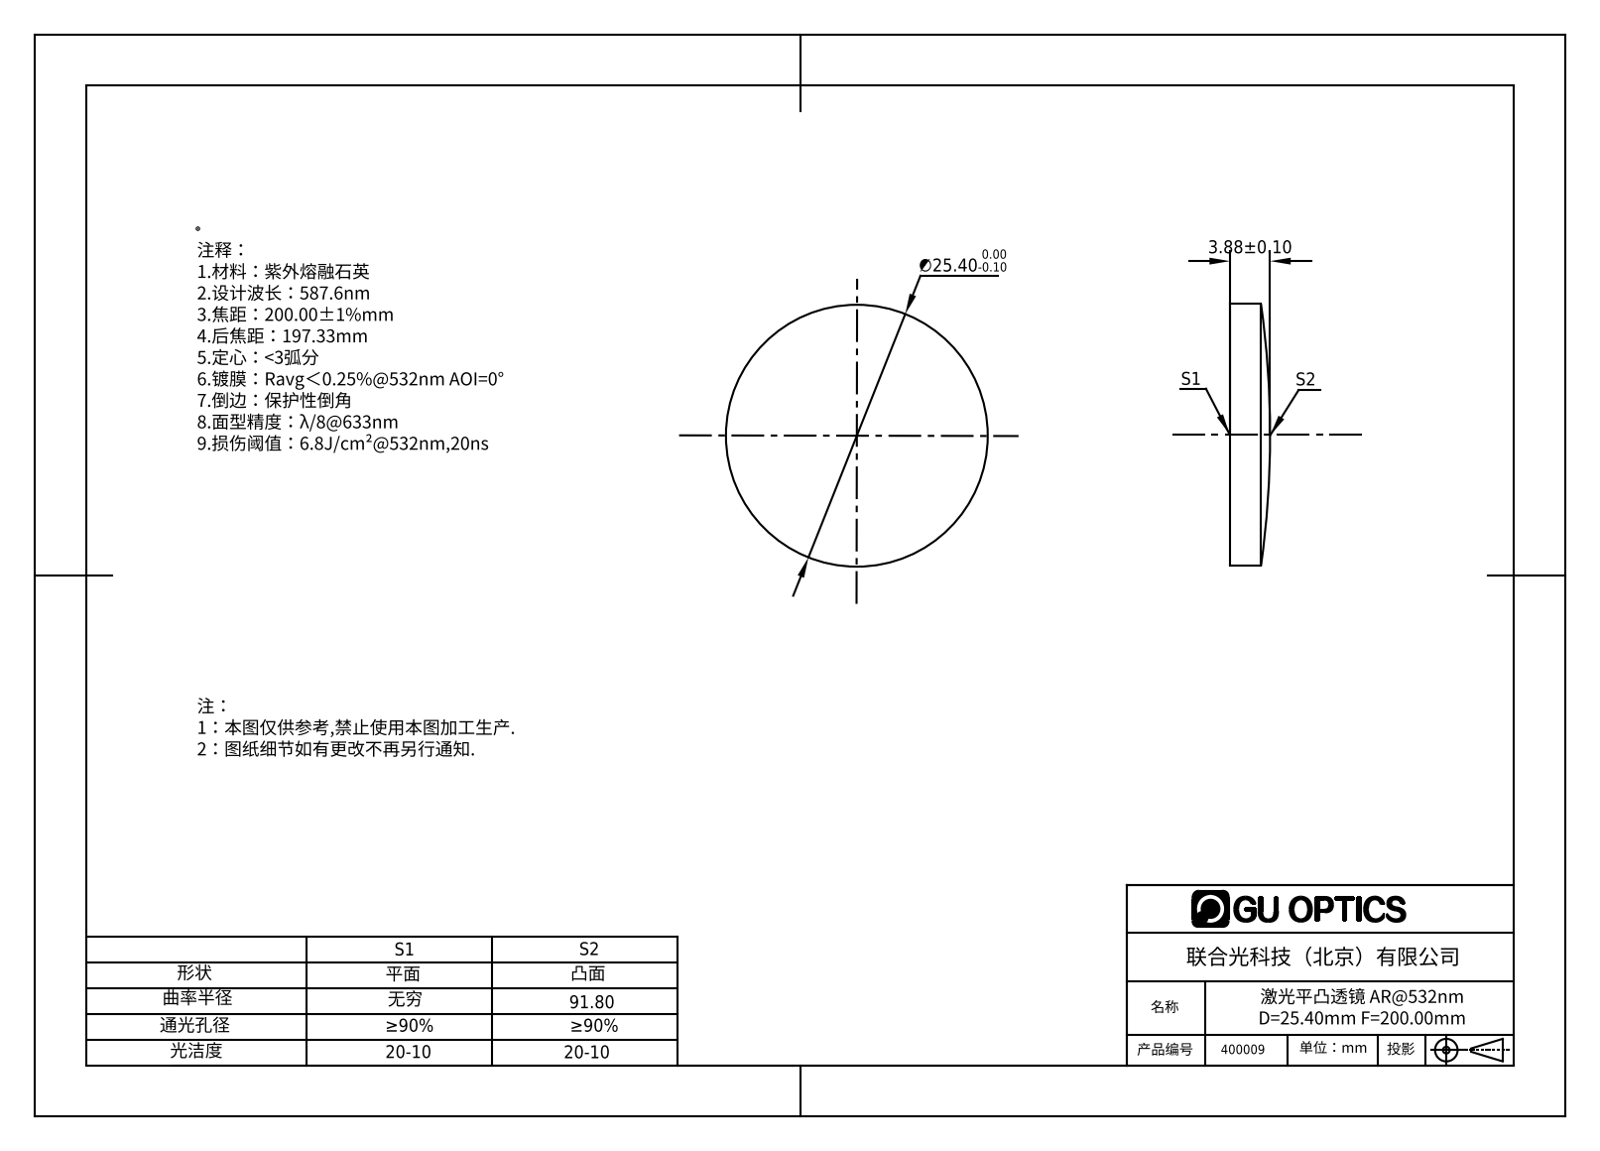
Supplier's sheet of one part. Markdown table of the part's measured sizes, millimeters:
| quantity | value |
| --- | --- |
| part name | 400003 |
| STEP written by | SolidWorks 2016 (AUTOMOTIVE_DESIGN) |
| units | millimeters |
| bodies | 1 solid, 5 faces (1 planar, 2 cylindrical, 2 other) |
| overall size | 25.4 × 25.4 × 3.88 |
| volume | 1 744 mm³ |
| surface area | 1 255 mm² |
| round bosses / shafts (diameter × count) | 25.4 × 1 |
